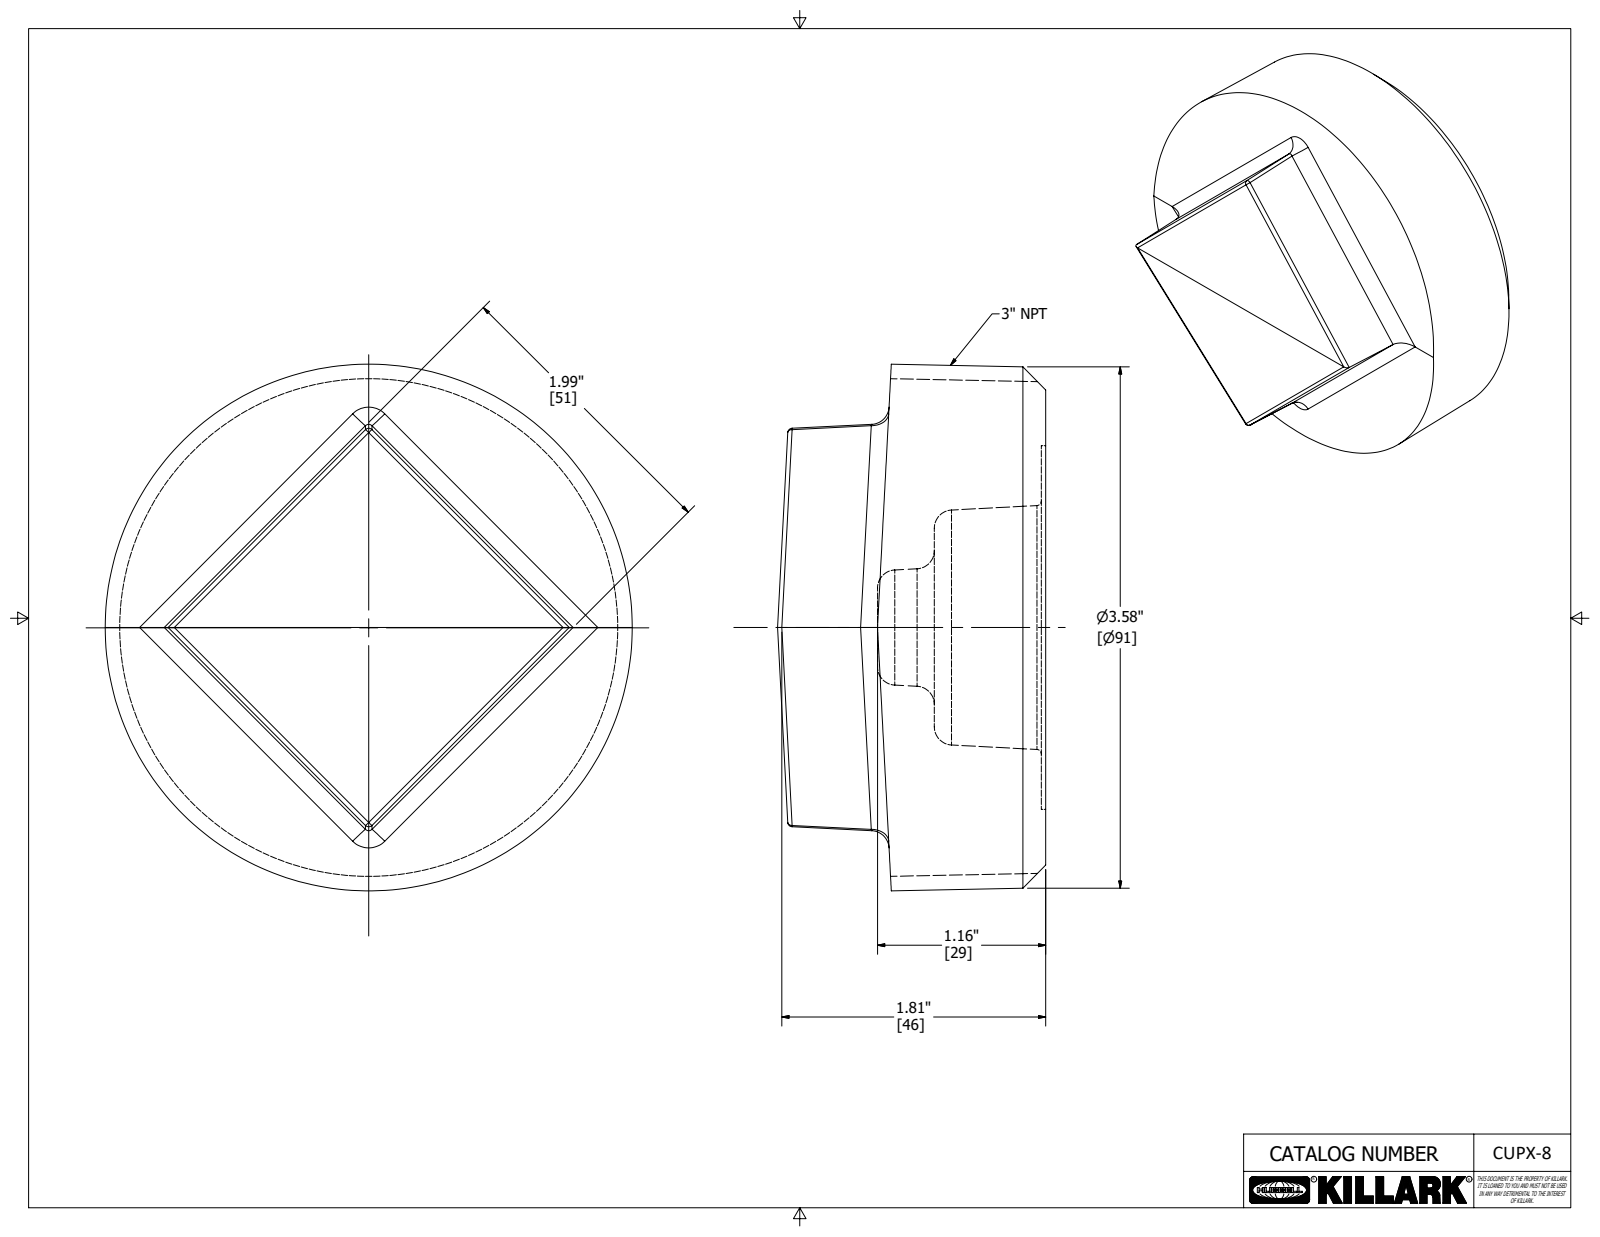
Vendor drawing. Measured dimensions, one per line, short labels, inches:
name: CUPX-8
written by: Autodesk Inventor 2020 (AUTOMOTIVE_DESIGN)
unit: in
bodies: 1 solid, 35 faces (12 planar, 11 cylindrical, 12 other)
size: 3.625 × 3.621 × 1.844
volume: 12.05 in³; area: 40.75 in²
holes: 1× ⌀2.5
rounds: 6× R0.031, 4× R0.125
face distances: 0.03, 0.687, 0.687, 0.736, 0.766, 0.391, 1.126, 1.156
